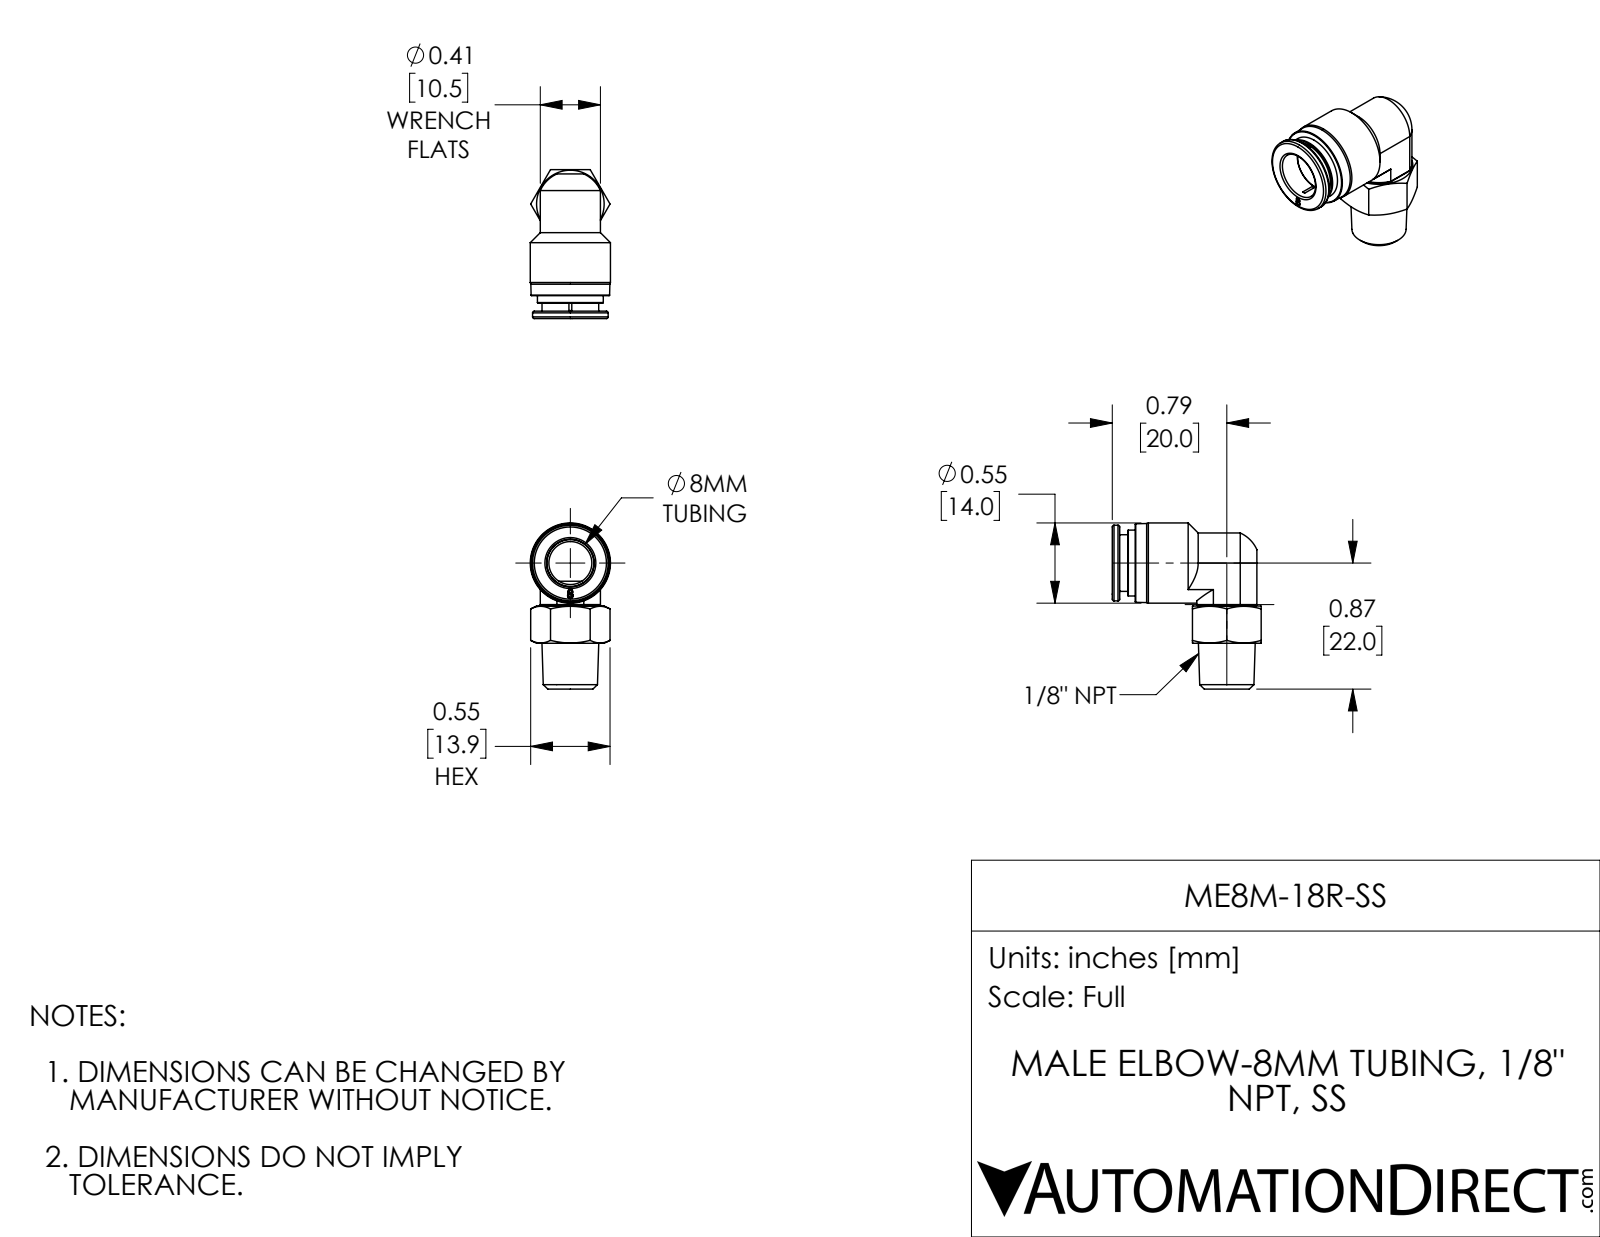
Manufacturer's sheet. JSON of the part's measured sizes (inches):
{"part_name": "ME8M-18R-SS", "step_written_by": "SolidWorks 2017 (AUTOMOTIVE_DESIGN)", "units": "inches", "bodies": {"solids": 2, "faces": 118, "planar": 31, "cylindrical": 34, "other": 53}, "overall_size": [1.142, 1.024, 0.551], "volume_in3": 0.195, "surface_area_in2": 4.967, "round_holes": [[0.157, 1], [0.238, 1], [0.295, 1], [0.323, 1], [0.327, 1], [0.394, 1]], "round_bosses_or_shafts": [[0.551, 1], [0.52, 1], [0.453, 1], [0.39, 1], [0.236, 1]], "partial_cylinders_radius": [[0.008, 4], [0.207, 1], [0.226, 1]], "face_to_face_distances": [0.472, 0.051, 0.106, 0.413, 0.03, 0.443, 0.157, 0.837, 0.943, 0.994]}
